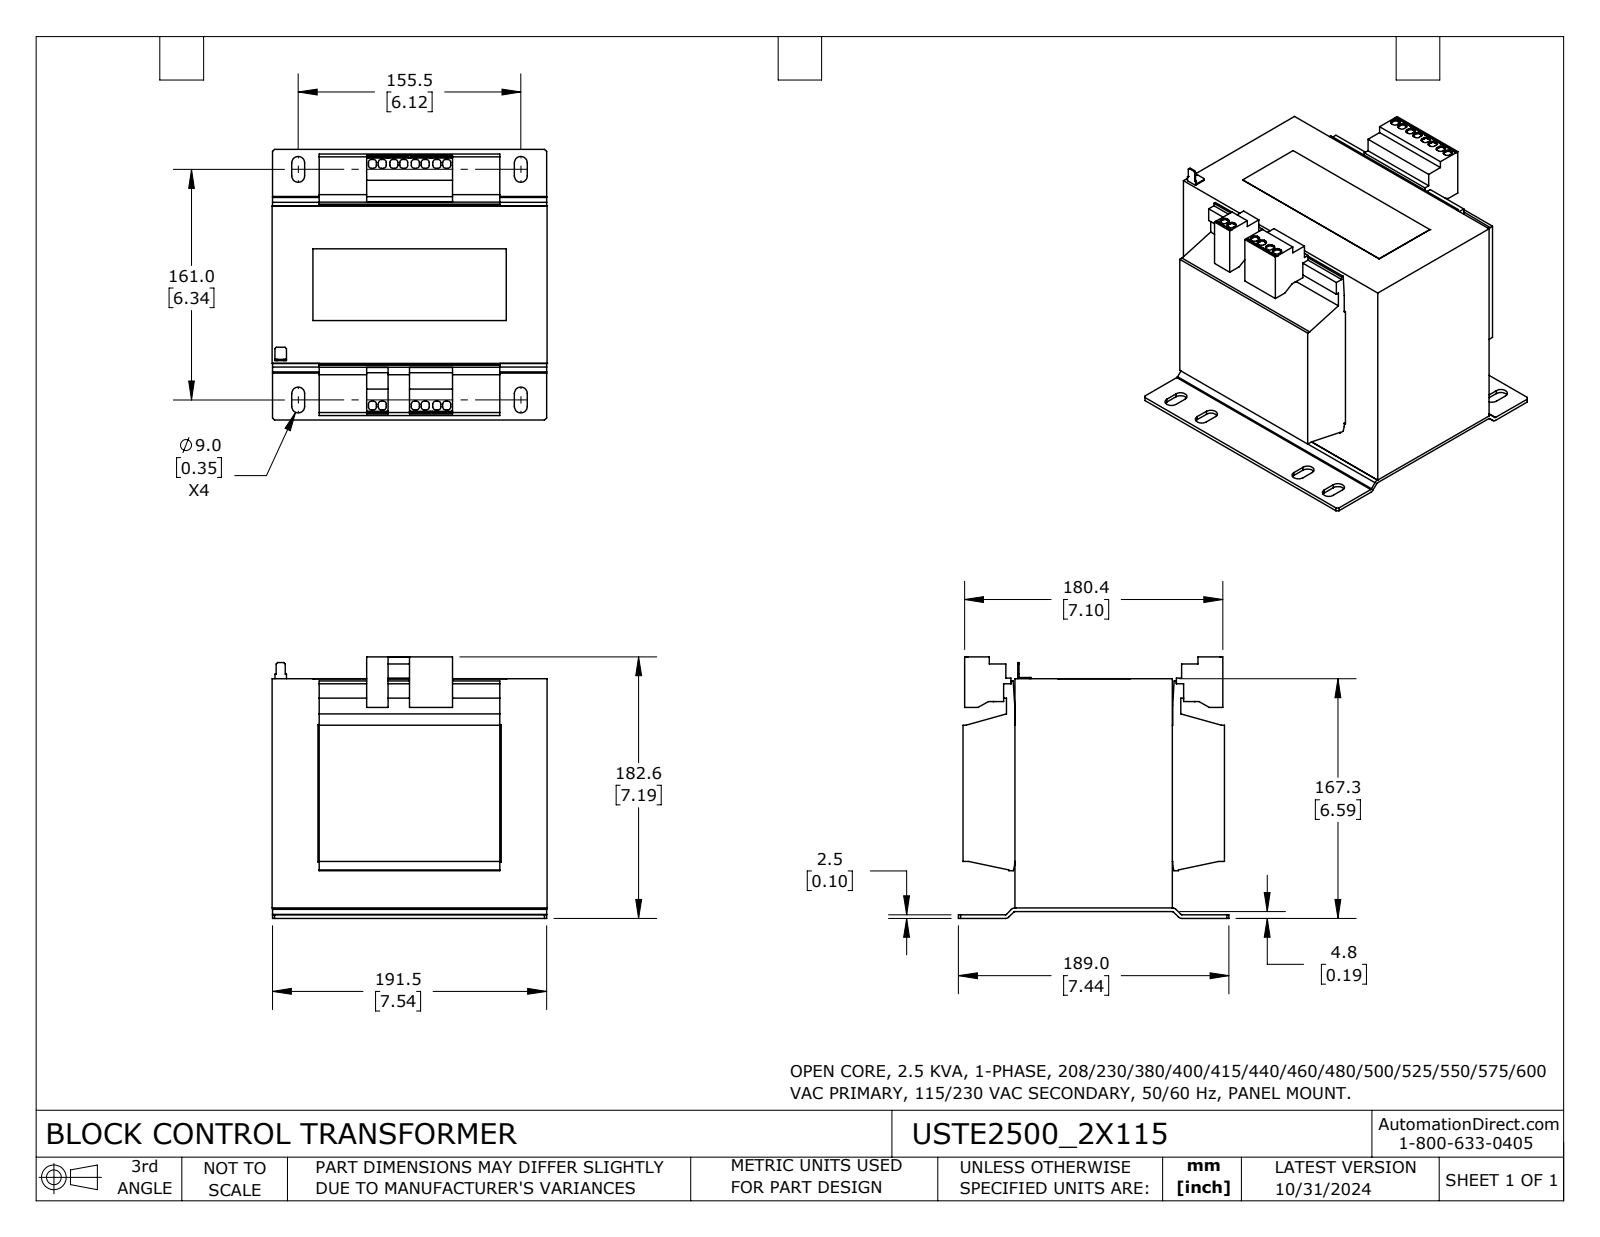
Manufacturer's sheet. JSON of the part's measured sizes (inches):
{"part_name": "USTE2500_2X115", "step_written_by": "SolidWorks 2023 (CONFIG_CONTROL_DESIGN)", "units": "inches", "bodies": {"solids": 1, "faces": 447, "planar": 367, "cylindrical": 80, "other": 0}, "overall_size": [7.559, 7.441, 7.19], "volume_in3": 274, "surface_area_in2": 492.5, "partial_cylinders_radius": [[0.087, 56], [0.177, 16], [0.039, 4], [0.138, 4]], "face_to_face_distances": [1.295, 6.264, 1.26, 1.431, 5.758, 6.299, 0.035, 5.004, 4.327, 4.969]}
